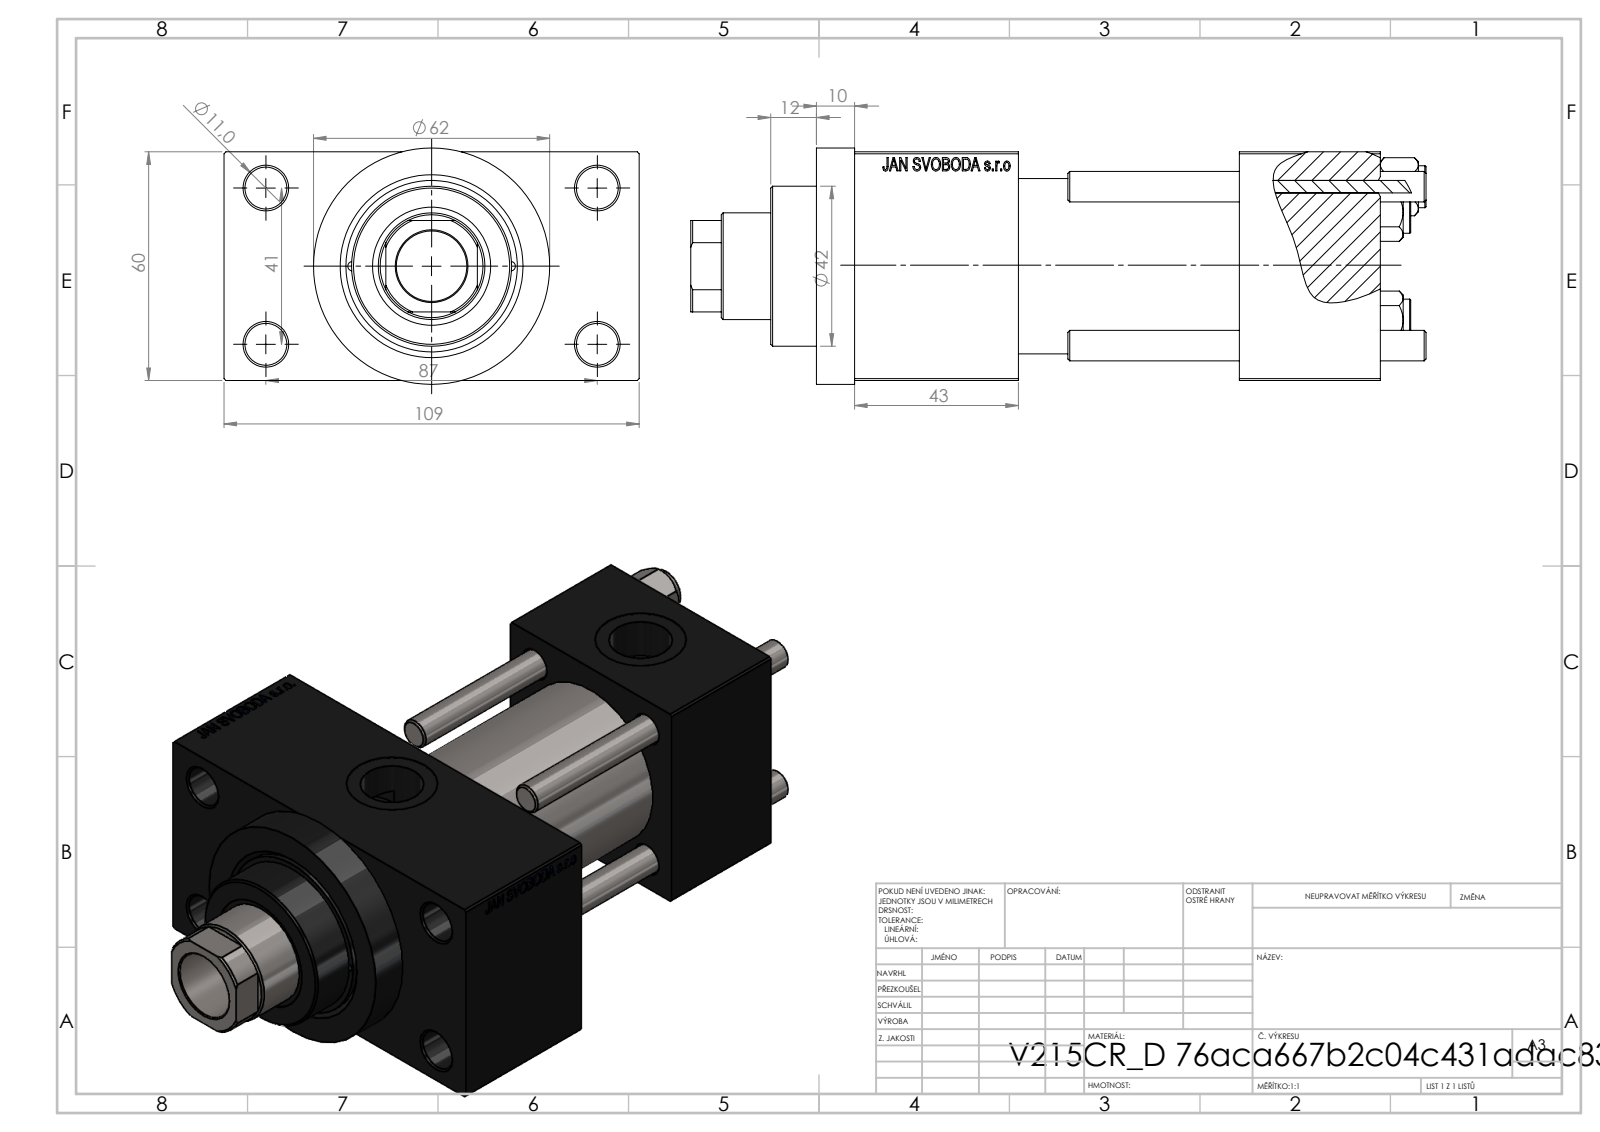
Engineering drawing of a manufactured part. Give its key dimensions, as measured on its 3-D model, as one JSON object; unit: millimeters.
{"part_name": "V215CR_VCP_D; NUT_M5_D; V215CR_D; V215_VC_A (+1 more)", "step_written_by": "SolidWorks 2019 (CONFIG_CONTROL_DESIGN)", "units": "millimeters", "bodies": {"solids": 11, "faces": 1135, "planar": 506, "cylindrical": 103, "other": 526}, "overall_size": [193, 109, 62], "volume_mm3": 520316, "surface_area_mm2": 126926, "round_holes": [[8, 7], [11, 4], [16.66, 4], [24, 4], [7, 3], [2.5, 2], [18.5, 1], [28, 1], [31, 1], [40, 1], [45, 1]], "round_bosses_or_shafts": [[11, 4], [62, 1], [46, 1], [42, 1]], "partial_cylinders_radius": [[13.5, 1]], "face_to_face_distances": [60, 58, 24.5, 84.5, 43, 37, 95, 101, 138, 109], "hole_center_spacings": [35.64, 20.85, 22.65, 29.49, 30.62, 41.7, 46.53, 47.15]}
